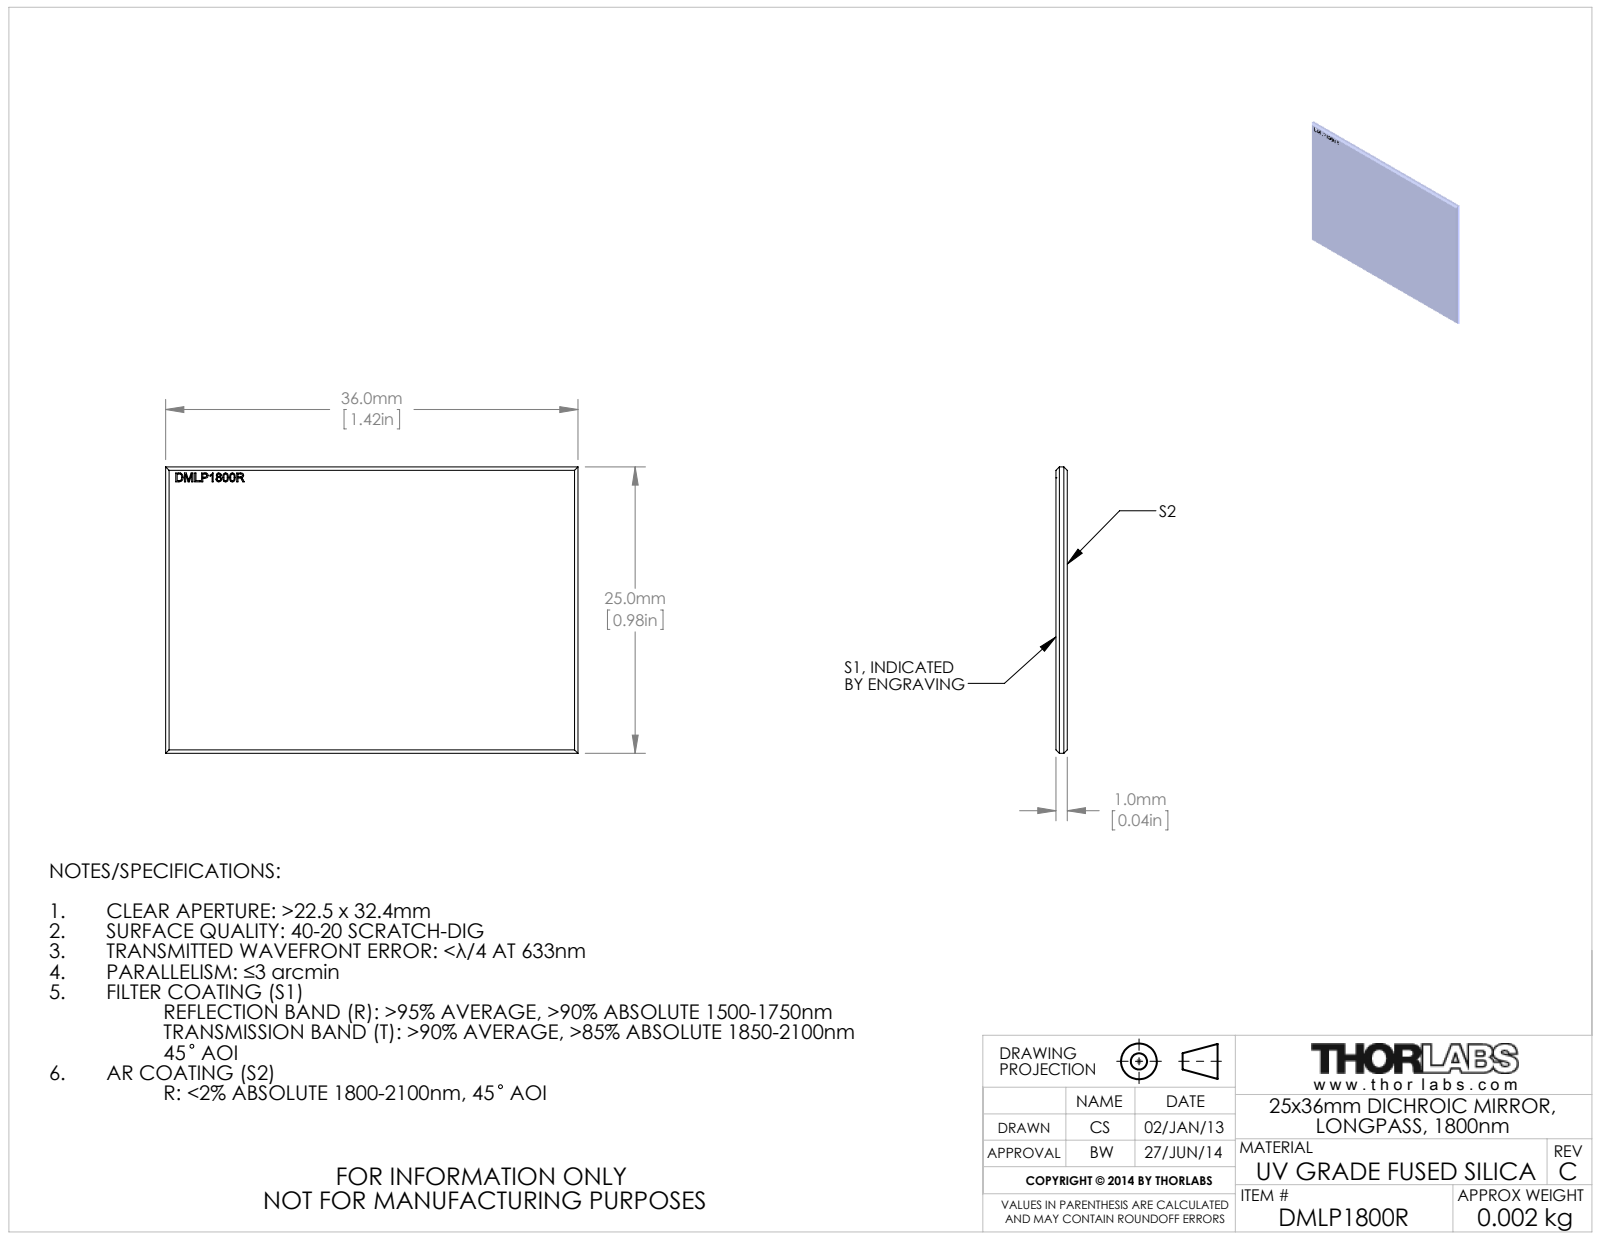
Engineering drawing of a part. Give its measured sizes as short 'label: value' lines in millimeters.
name: TTN007447-E0W
written by: SolidWorks 2012 (CONFIG_CONTROL_DESIGN)
unit: mm
bodies: 1 solid, 141 faces (79 planar, 0 cylindrical, 62 other)
size: 36 × 25 × 1
volume: 889 mm³; area: 1 879 mm²
face distances: 1, 17.95, 17.96, 25, 25.74, 25.73, 36, 0.99, 1.49, 0.75
